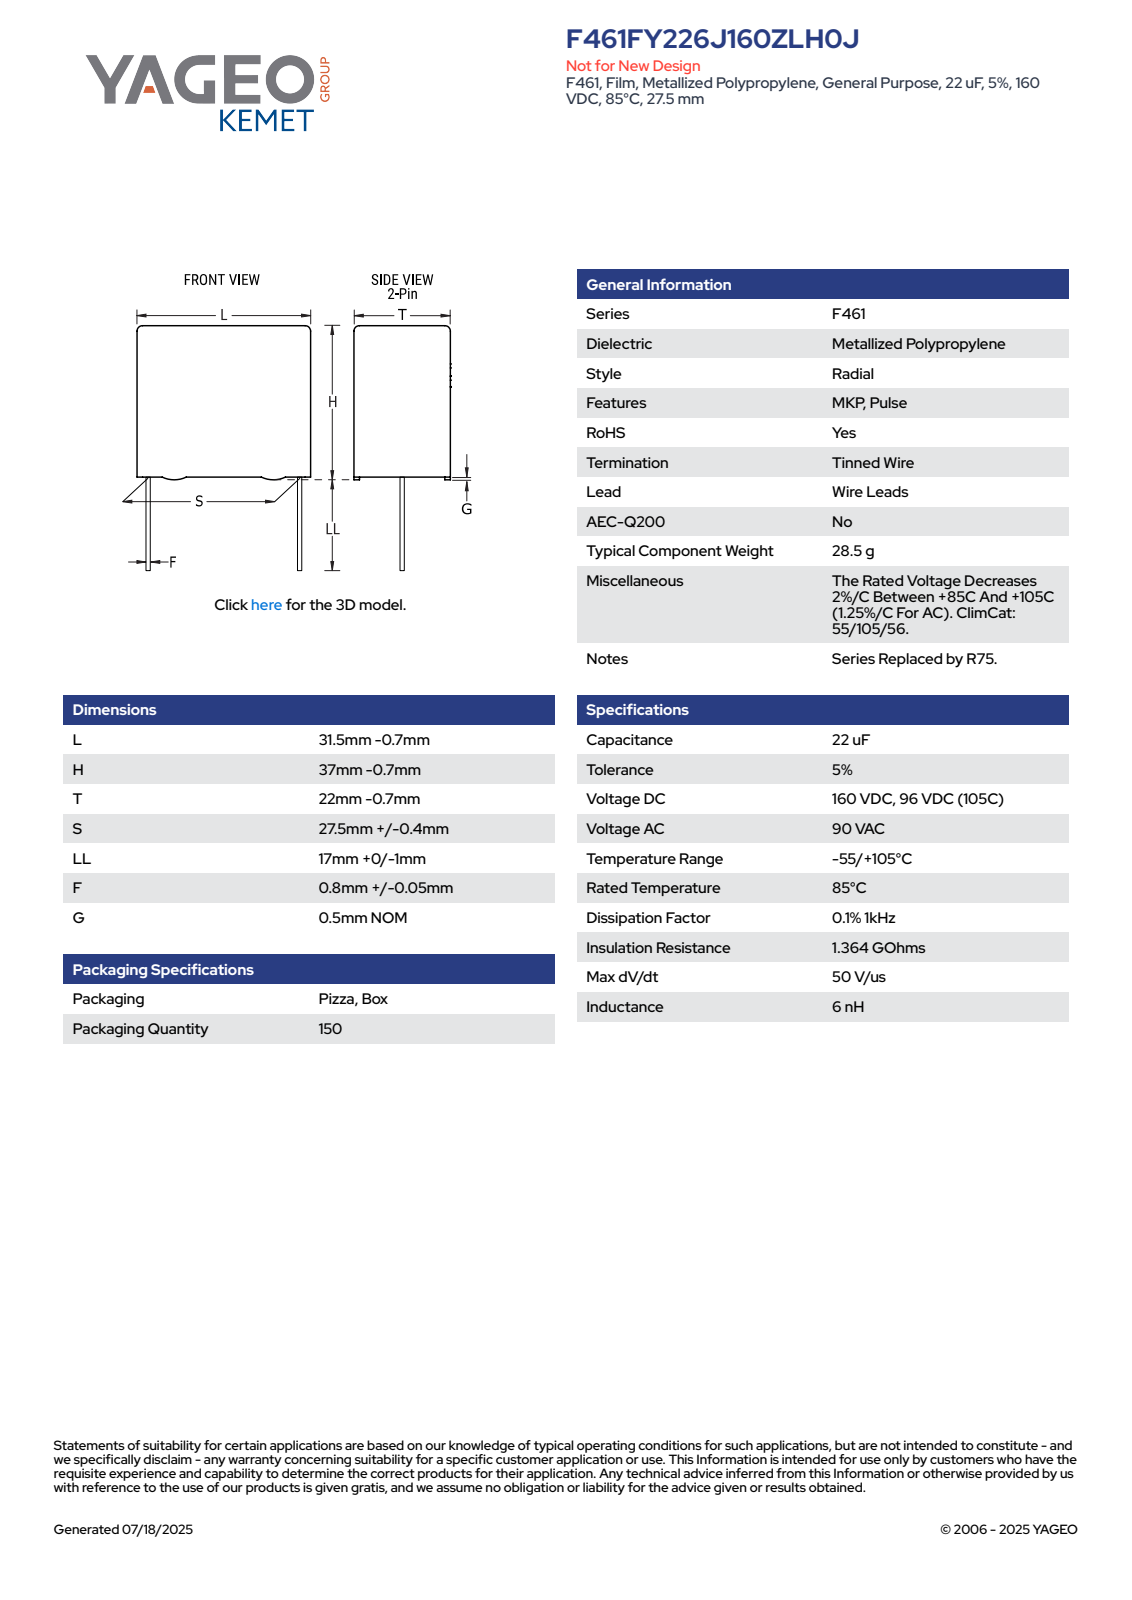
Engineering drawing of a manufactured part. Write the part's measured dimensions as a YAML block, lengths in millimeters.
part_name: "CFR_RBG_31.5X37X22_L30.8H36.3T21.3S27.5LL17F0.85G0.5"
step_written_by: "SolidWorks 2014 (AUTOMOTIVE_DESIGN)"
units: millimeters
bodies: {solids: 4, faces: 89, planar: 81, cylindrical: 8, other: 0}
overall_size: [53.3, 30.8, 21.3]
volume: 23513
surface_area: 5239
round_bosses_or_shafts:
  - {diameter: 0.85, count: 2}
partial_cylinders:
  - {radius: 0.5, count: 4}
face_to_face_distances: [21.3, 30.8, 35.8, 0.5, 36.3, 1.21, 20.09, 18.88, 16.82, 16.83]
